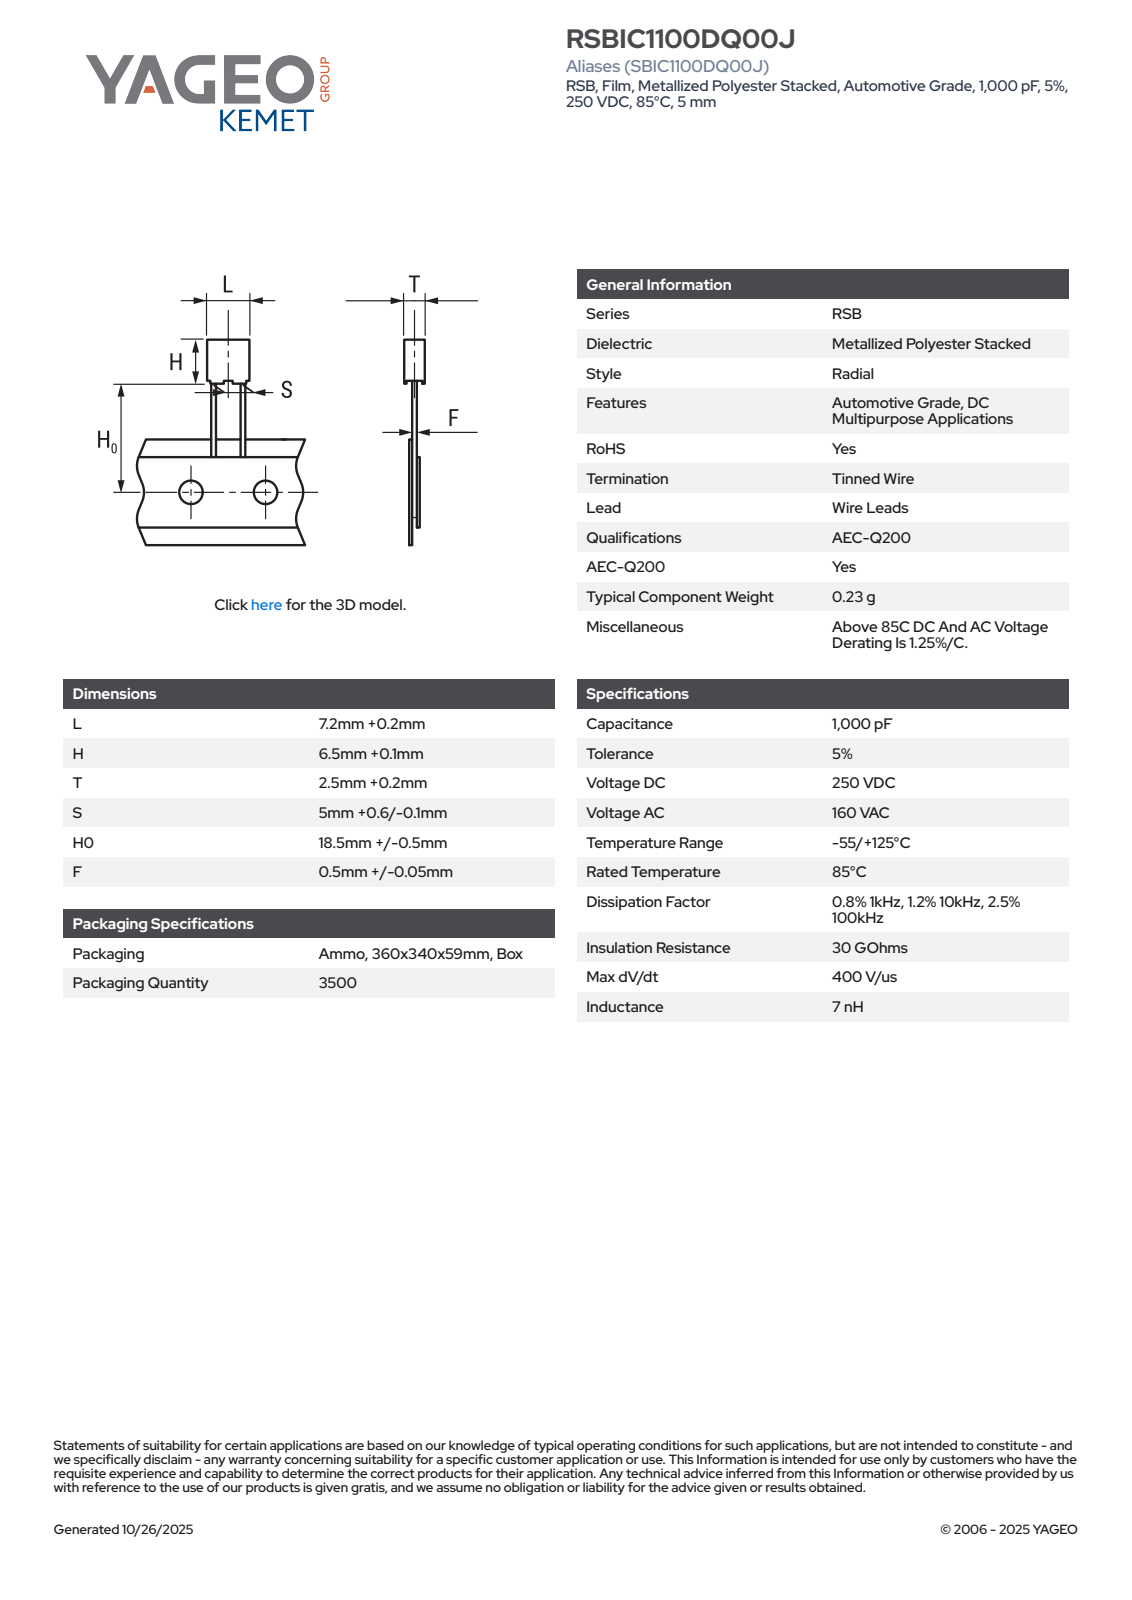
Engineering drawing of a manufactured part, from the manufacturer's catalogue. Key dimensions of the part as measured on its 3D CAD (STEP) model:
Part name (STEP PRODUCT): CFR_RB3_7.2X6.5X2.5_L7.4H6.6T2.7S5H019F0.65
STEP written by: SolidWorks 2014 (AUTOMOTIVE_DESIGN)
Units: millimetres
Bodies: 4 solids, 85 faces (77 planar, 8 cylindrical, 0 other)
Overall size (bounding box): 25.6 × 7.4 × 2.71
Volume: 132 mm³ · Surface area: 266 mm²
Round bosses / shafts (diameter × count): ⌀0.65 ×2
Partial cylindrical surfaces — rounded edges, fillets, slot ends (radius × count): R0.5 ×4
Main face-to-face distances: 2.7, 7.4, 5.85, 2.45, 2.2, 0.75, 6.6, 7.15, 6.9, 2.46
